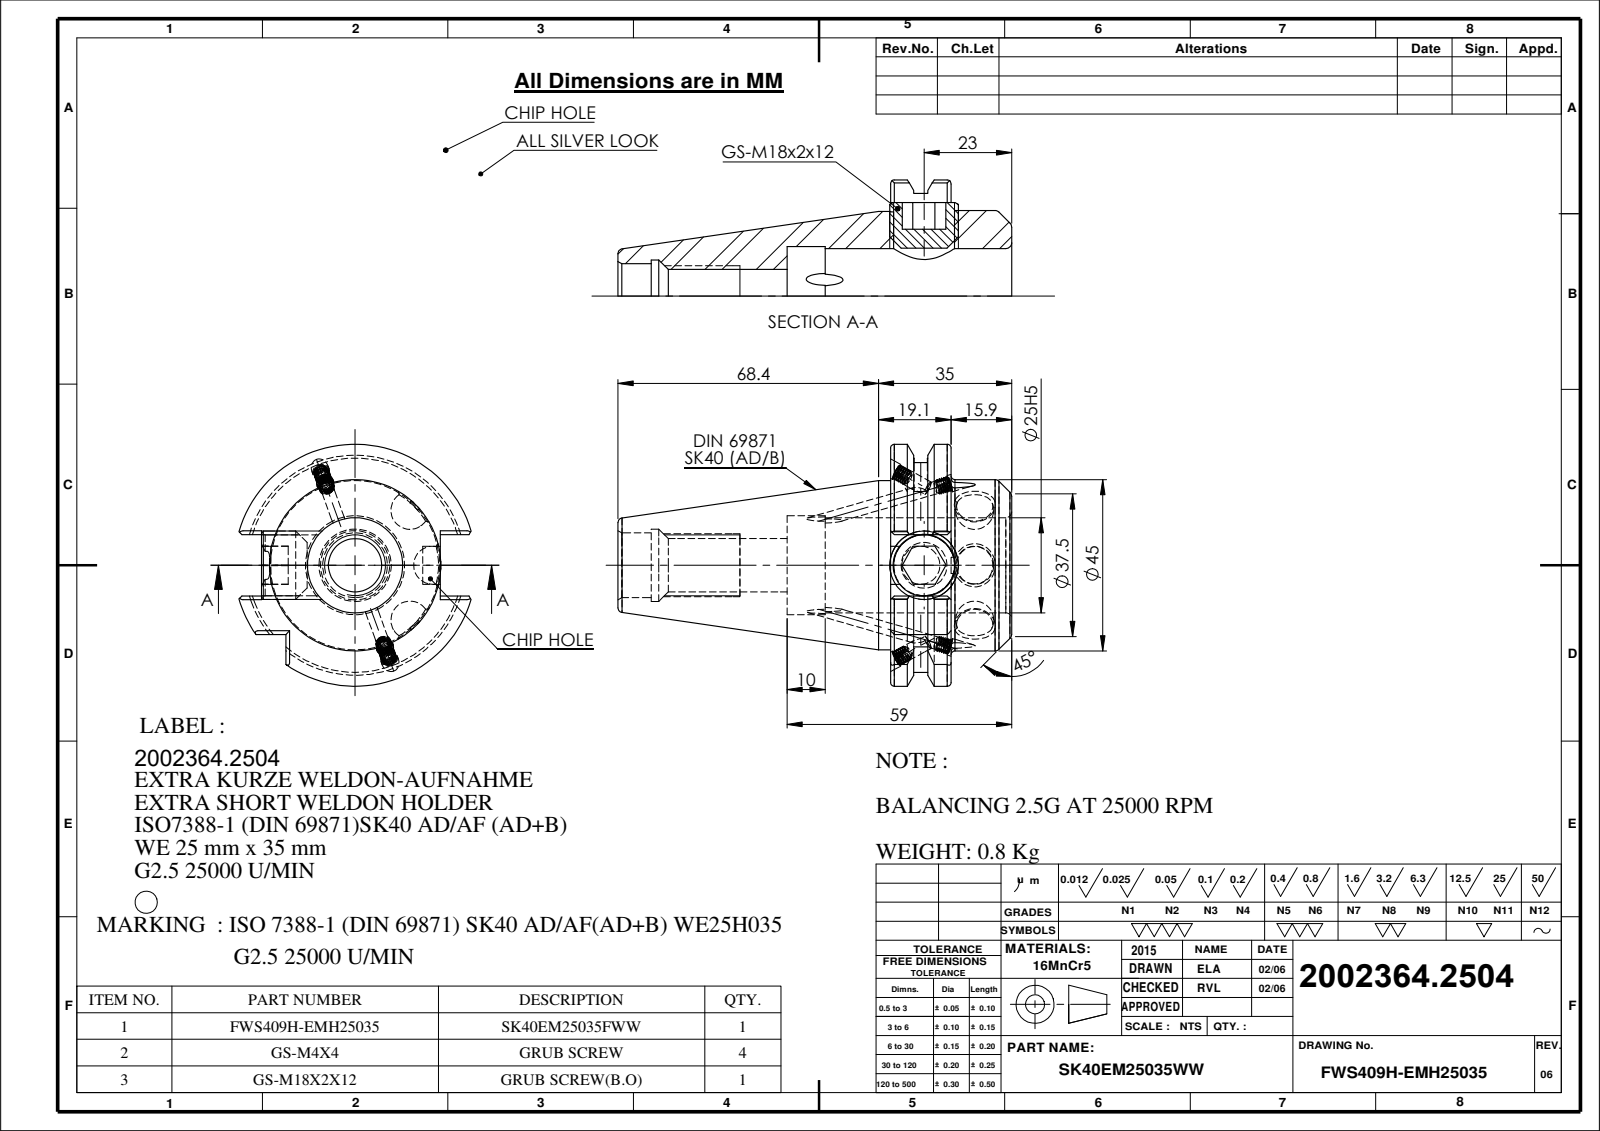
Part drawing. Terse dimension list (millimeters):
name: GS-M18X2X12; 91406-WE725035; SK40EM25035FWW-M&G-R07; GS-M4X4_DIN 913 - M4 x 4-N (+1 more)
written by: SolidWorks 2018 (CONFIG_CONTROL_DESIGN)
unit: mm
bodies: 6 solids, 363 faces (104 planar, 89 cylindrical, 170 other)
size: 103.4 × 63.55 × 61
volume: 97 511 mm³; area: 28 353 mm²
holes: 4× ⌀4.5, 2× ⌀3.3, 1× ⌀4, 1× ⌀10, 1× ⌀14, 1× ⌀16, 1× ⌀17, 1× ⌀19, 1× ⌀25, 1× ⌀26
bosses: 4× ⌀4, 1× ⌀45, 1× ⌀44.45, 1× ⌀18
rounds: 1× R28.12, 1× R31.77
face distances: 15.9, 31.8, 27.2, 43.1, 59, 16.1, 47, 44.4, 71.6, 87.5
hole spacings: 0.85
